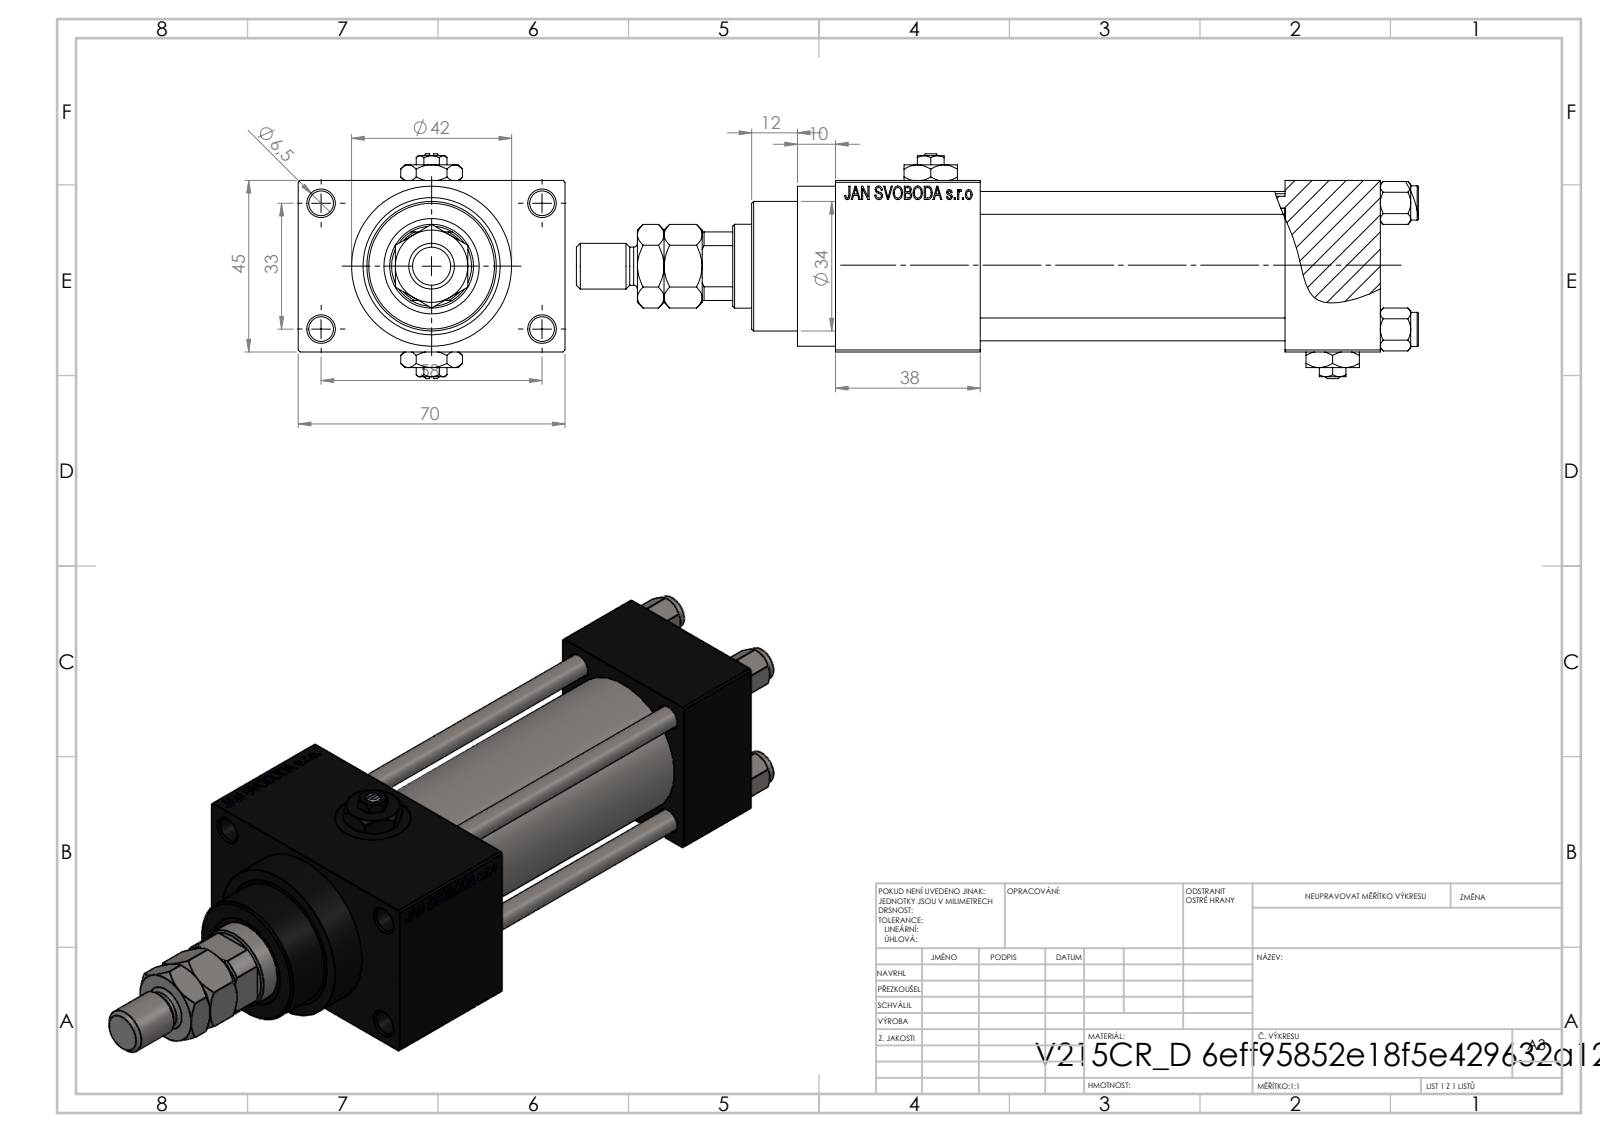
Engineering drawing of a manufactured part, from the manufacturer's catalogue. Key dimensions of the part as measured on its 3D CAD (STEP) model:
Part name (STEP PRODUCT): V215CR_D_Body; V215_VC_A; NUT_M5_D; V215CR_VCP_D (+3 more)
STEP written by: SolidWorks 2019 (CONFIG_CONTROL_DESIGN)
Units: millimetres
Bodies: 14 solids, 1238 faces (555 planar, 93 cylindrical, 590 other)
Overall size (bounding box): 221 × 70 × 59
Volume: 277 814 mm³ · Surface area: 93 808 mm²
Round holes (diameter × count): ⌀6 ×4, ⌀6.5 ×4, ⌀7 ×2, ⌀13.16 ×2, ⌀20 ×2, ⌀10.5 ×1, ⌀22 ×1, ⌀24 ×1, ⌀25 ×1, ⌀32 ×1, ⌀33 ×1
Round bosses / shafts (diameter × count): ⌀9 ×4, ⌀42 ×1, ⌀38 ×1, ⌀34 ×1, ⌀12 ×1, ⌀10 ×1
Partial cylindrical surfaces — rounded edges, fillets, slot ends (radius × count): R10.5 ×1
Main face-to-face distances: 45, 25, 12.5, 57.5, 80, 105, 118, 70, 38, 143
Hole centre spacings: 12.4, 23.48, 33.2, 33.37, 35.35, 45.6, 56.35, 33
